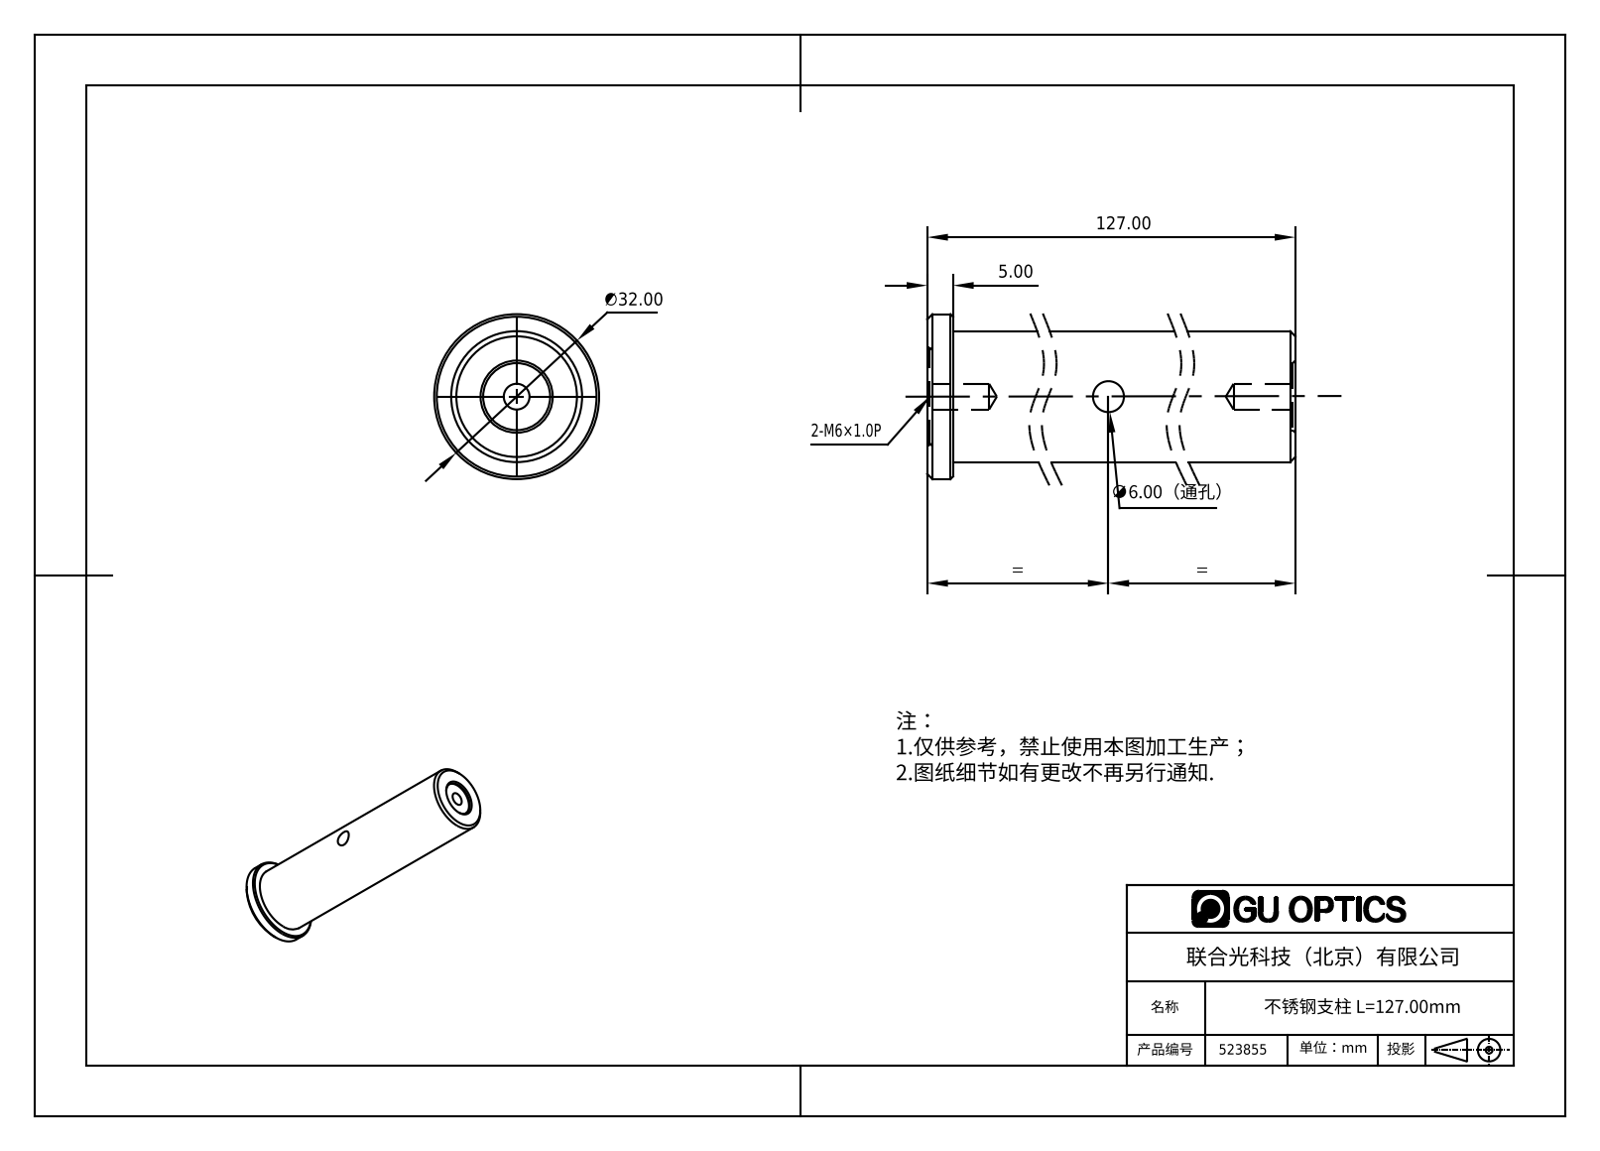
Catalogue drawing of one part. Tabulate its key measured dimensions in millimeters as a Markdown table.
| quantity | value |
| --- | --- |
| part name | 523855 |
| STEP written by | SolidWorks 2016 (AUTOMOTIVE_DESIGN) |
| units | millimeters |
| bodies | 1 solid, 33 faces (5 planar, 14 cylindrical, 14 other) |
| overall size | 127 × 32 × 32 |
| volume | 64 160 mm³ |
| surface area | 12 547 mm² |
| round holes (diameter × count) | 5 × 1, 6 × 1, 13 × 1, 19 × 1 |
| round bosses / shafts (diameter × count) | 32 × 1, 25.4 × 1 |
| main face-to-face distances | 1, 126, 127, 5, 122, 4, 125, 121 |
